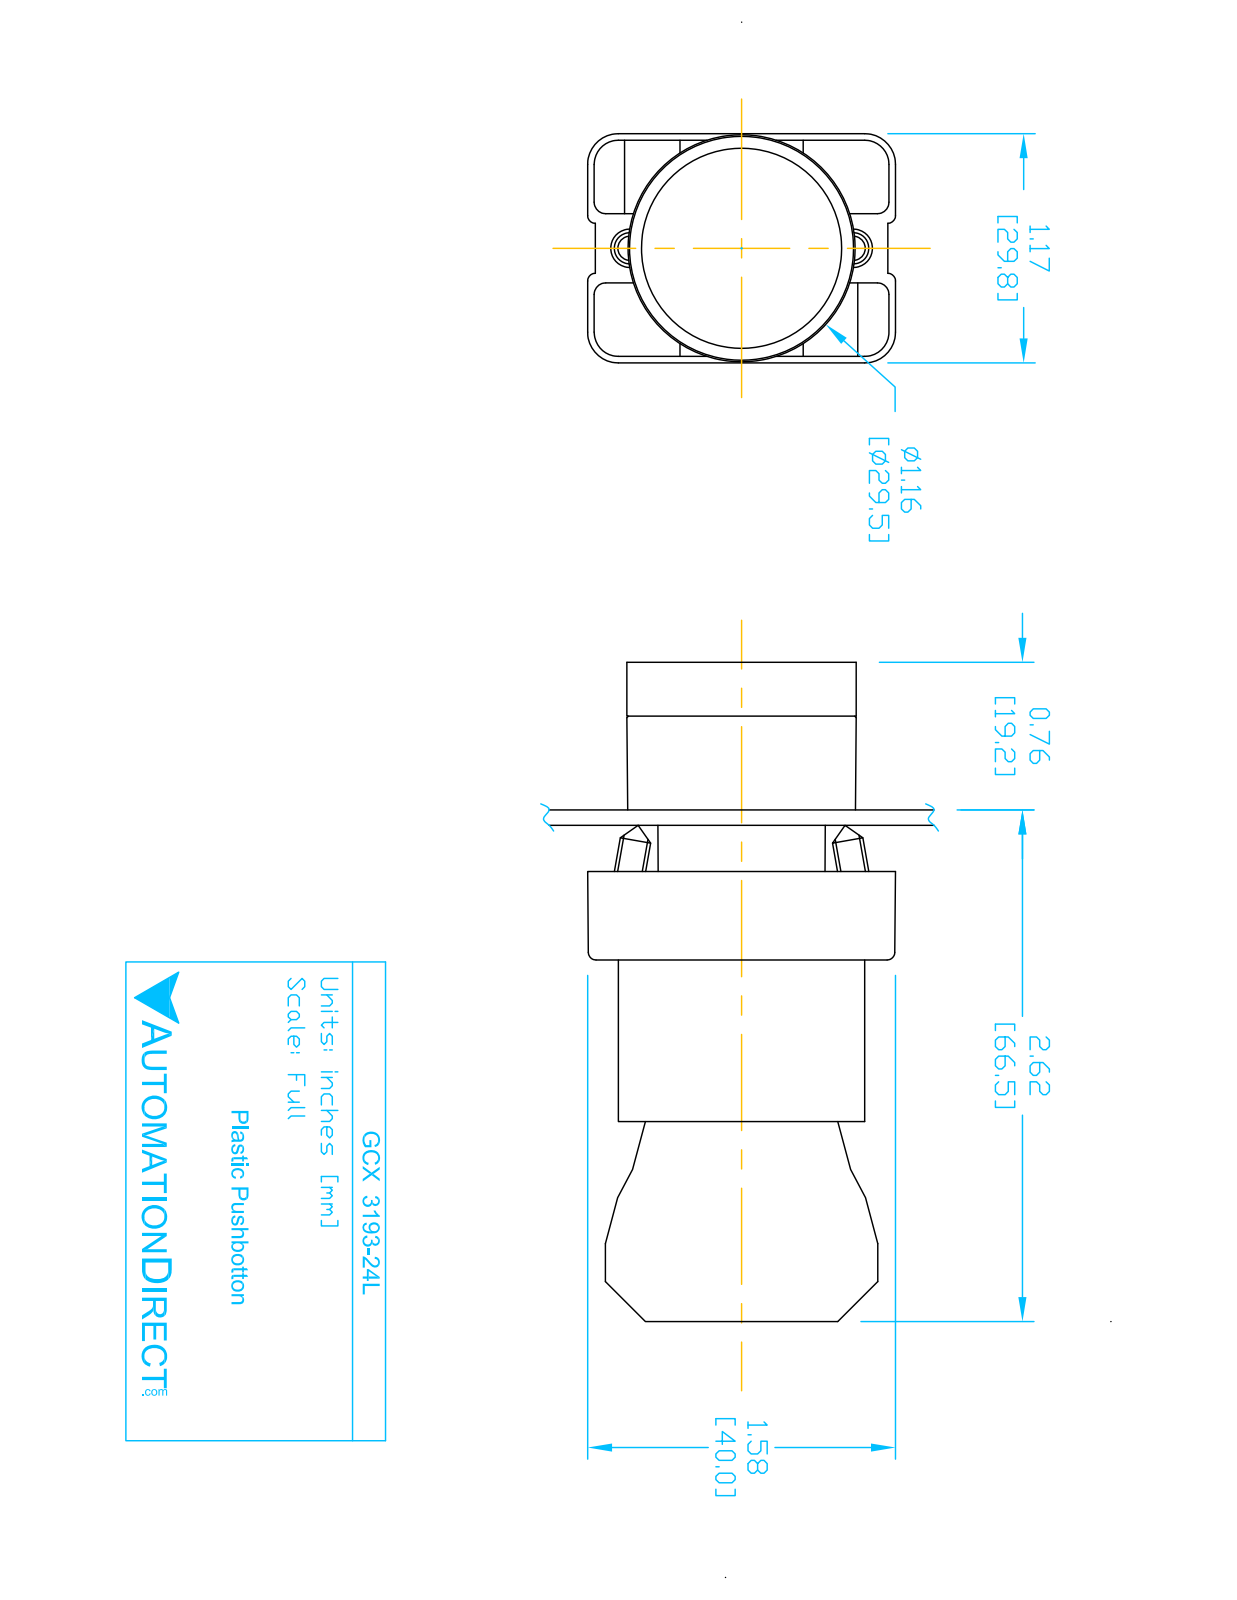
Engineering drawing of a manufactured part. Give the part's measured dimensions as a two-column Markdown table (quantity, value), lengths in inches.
| quantity | value |
| --- | --- |
| part name | ECX1050; ECX3029-2; GCX3193-24L; CONTACT BLOCK (+1 more) |
| STEP written by | SolidWorks 2016 (AUTOMOTIVE_DESIGN) |
| units | inches |
| bodies | 8 solids, 431 faces (252 planar, 148 cylindrical, 31 other) |
| overall size | 3.319 × 1.581 × 1.177 |
| volume | 2.794 in³ |
| surface area | 38.77 in² |
| round holes (diameter × count) | 0.079 × 2, 0.124 × 2, 0.13 × 2, 0.087 × 1, 0.197 × 1, 0.469 × 1, 0.878 × 1, 0.888 × 1, 1.024 × 1 |
| round bosses / shafts (diameter × count) | 0.157 × 4, 1.175 × 1, 1.004 × 1, 0.945 × 1, 0.856 × 1, 0.78 × 1, 0.504 × 1 |
| partial cylindrical surfaces (radius × count) | 0.059 × 24, 0.041 × 12, 0.124 × 12, 0.157 × 12, 0.039 × 8, 0.128 × 2, 0.02 × 1, 0.063 × 1 |
| main face-to-face distances | 0.827, 0.579, 2.02, 1.193, 1.171, 0.276, 2.295, 1.469, 0.031, 0.033 |
| hole center spacings | 0.236, 0.544, 0.472, 0.49 |
